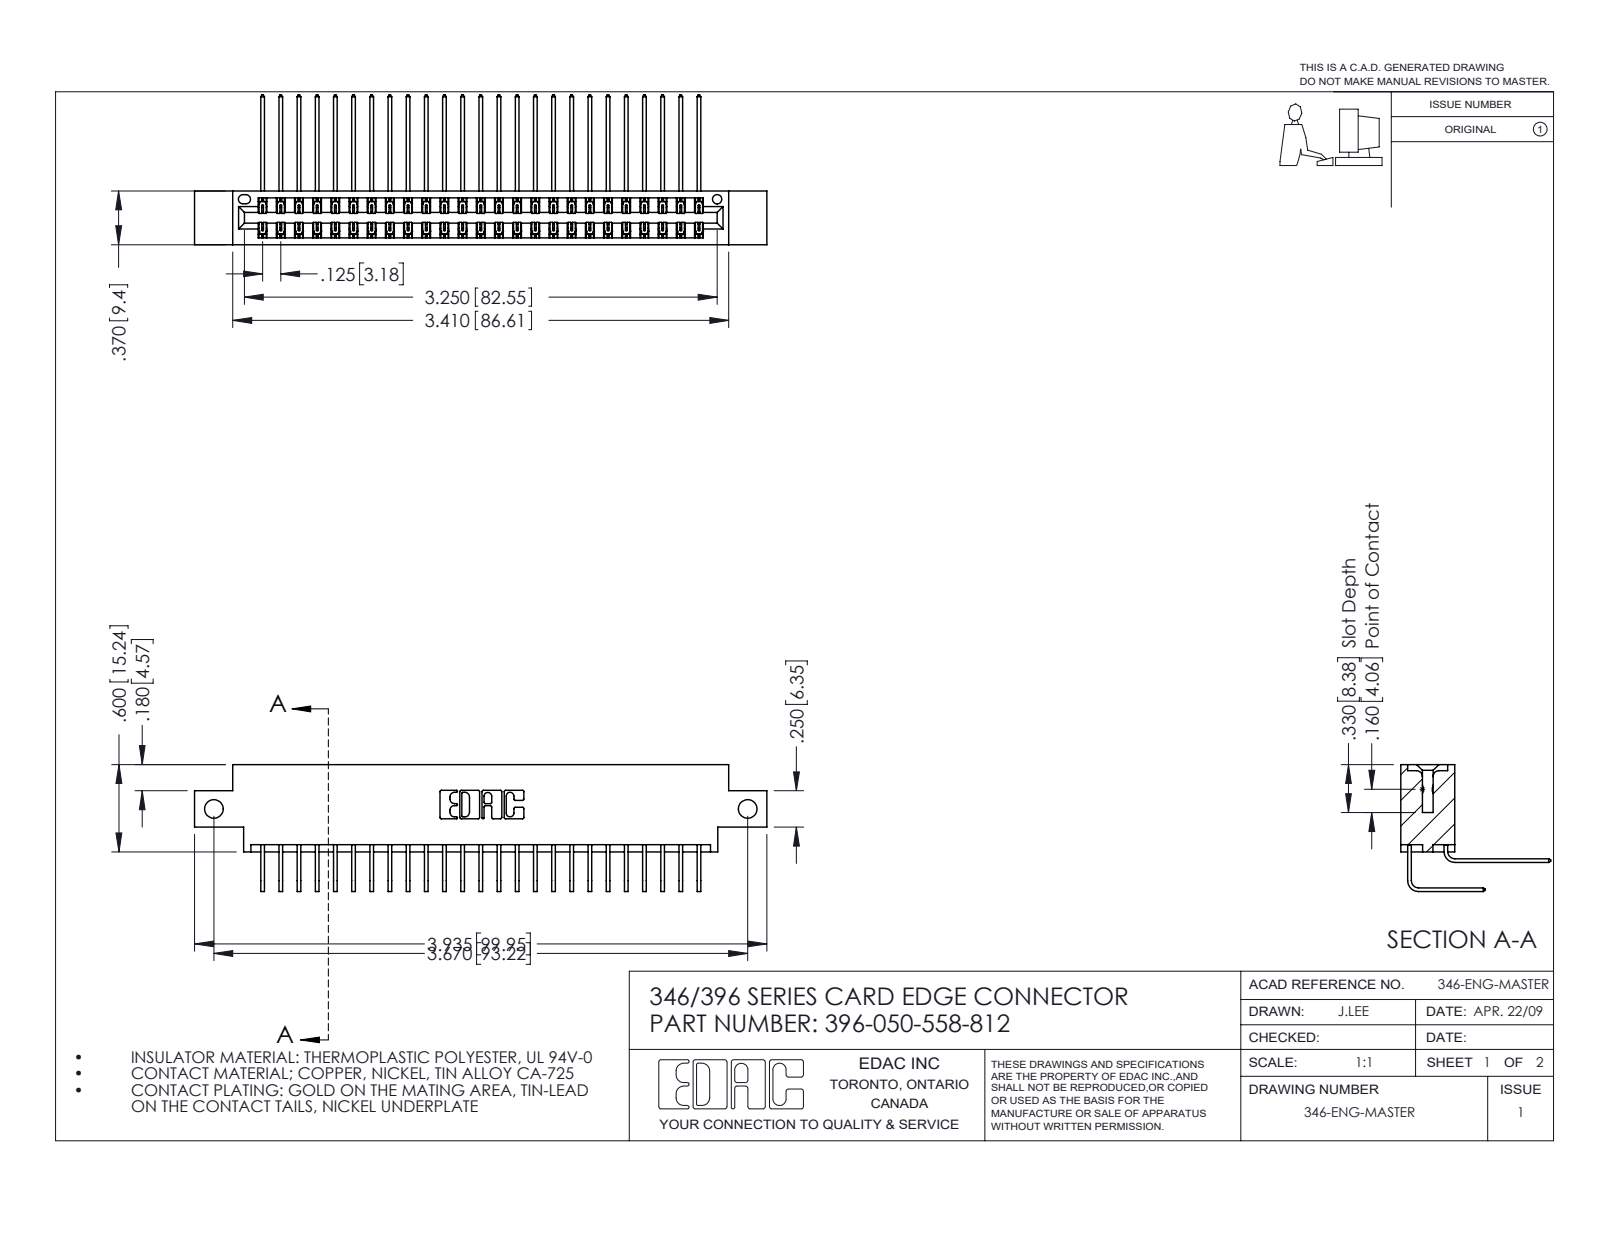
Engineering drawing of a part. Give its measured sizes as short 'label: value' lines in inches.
name: 345-292-001_558 559 Tail - 1; 346 Part_0.170 Offset - Side Mount; 345-292-001_558 Tail - 2; 396-050-558-812
written by: SolidWorks 2016 (CONFIG_CONTROL_DESIGN)
unit: in
bodies: 51 solids, 2826 faces (1930 planar, 896 cylindrical, 0 other)
size: 3.935 × 1.03 × 0.873
volume: 0.59 in³; area: 22.38 in²
holes: 2× ⌀0.128, 1× ⌀0.064
rounds: 75× R0.006, 22× R0.01, 6× R0.007, 6× R0.031, 3× R0.026, 2× R0.014, 2× R0.022, 2× R0.024
face distances: 0.322, 0.048, 0.025, 0.37, 0.25, 0.298, 0.072, 0.275, 0.148, 0.222
hole spacings: 3.67
